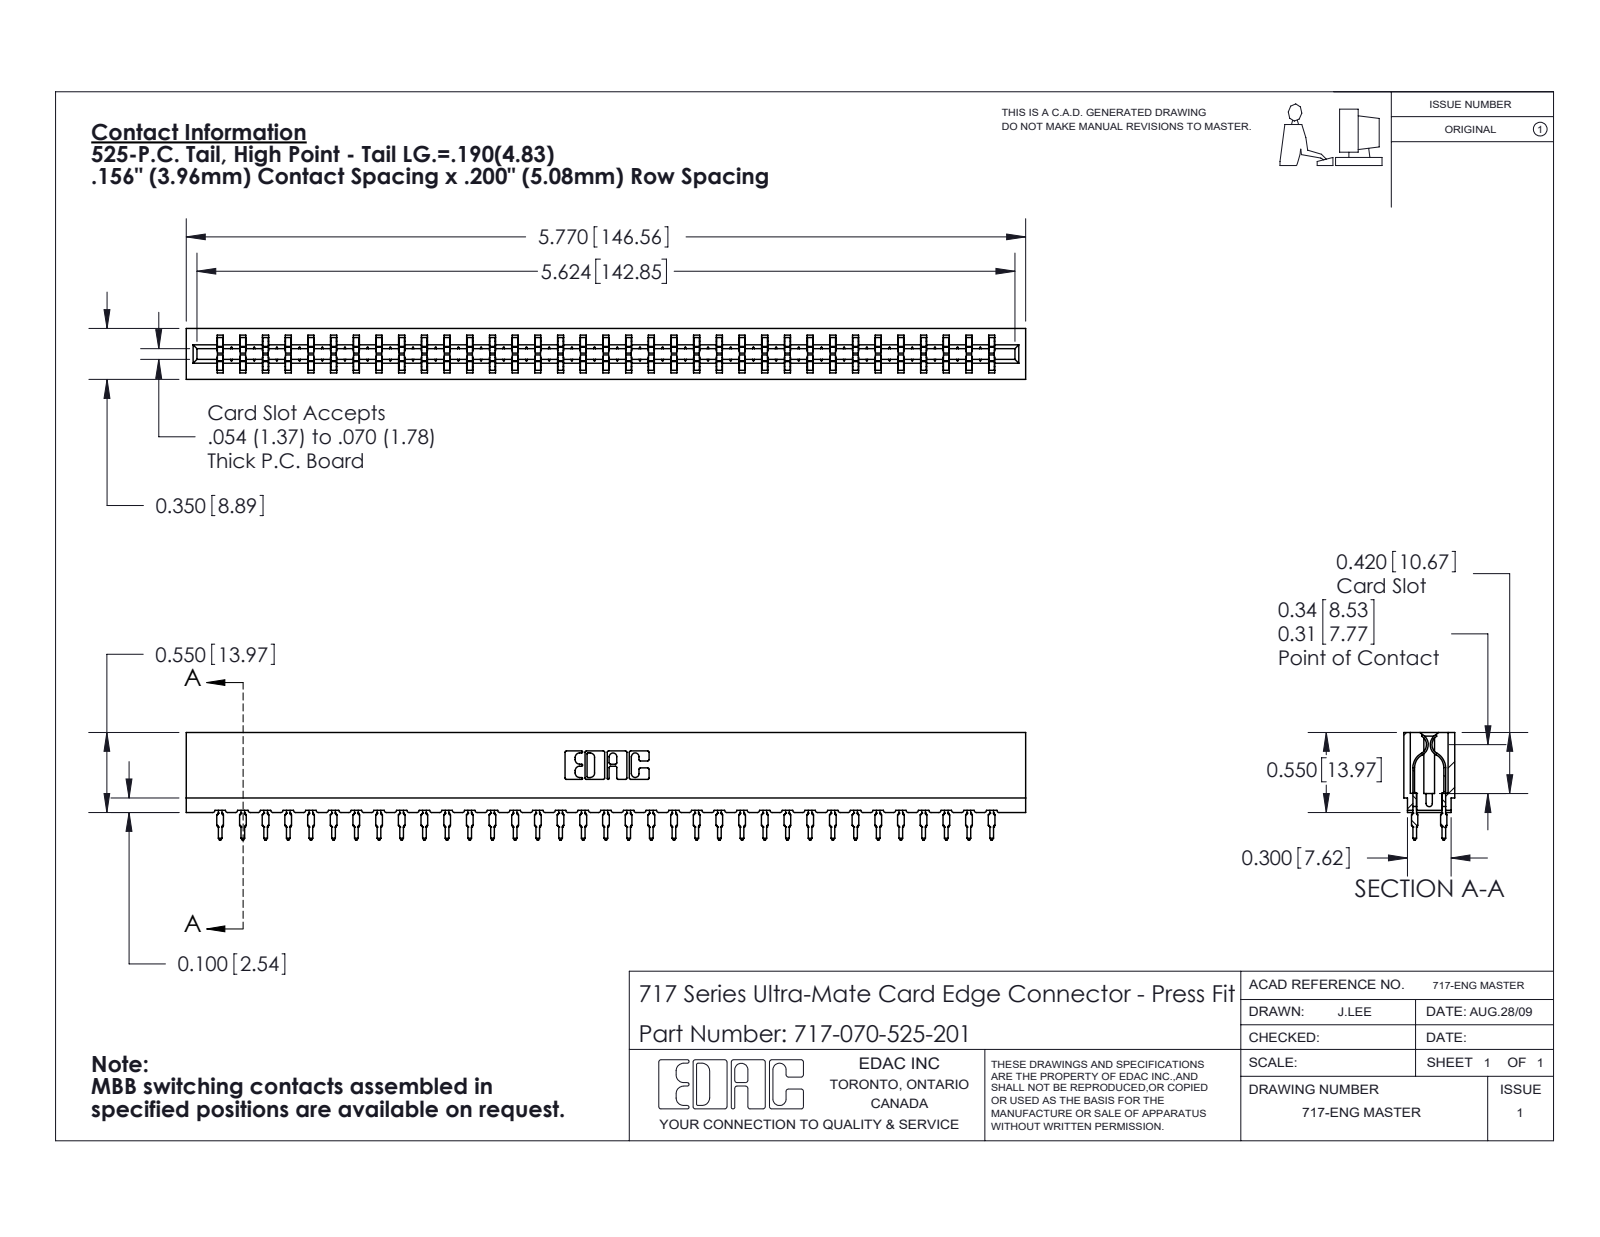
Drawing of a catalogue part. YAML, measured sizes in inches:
part_name: "717 Part_Insulator Option - 06; 745-292-001_525; 717-070-525-201"
step_written_by: "SolidWorks 2020 (CONFIG_CONTROL_DESIGN)"
units: inches
bodies: {solids: 71, faces: 6394, planar: 3309, cylindrical: 1265, other: 1820}
overall_size: [5.77, 0.739, 0.35]
volume: 0.776
surface_area: 29.87
partial_cylinders:
  - {radius: 0.021, count: 140}
  - {radius: 0.015, count: 70}
  - {radius: 0.01, count: 22}
  - {radius: 0.005, count: 8}
  - {radius: 0.011, count: 8}
  - {radius: 0.007, count: 6}
  - {radius: 0.031, count: 6}
  - {radius: 0.026, count: 3}
face_to_face_distances: [0.212, 0.138, 0.35, 0.063, 0.287, 0.076, 0.149, 0.074, 0.045, 0.305]
